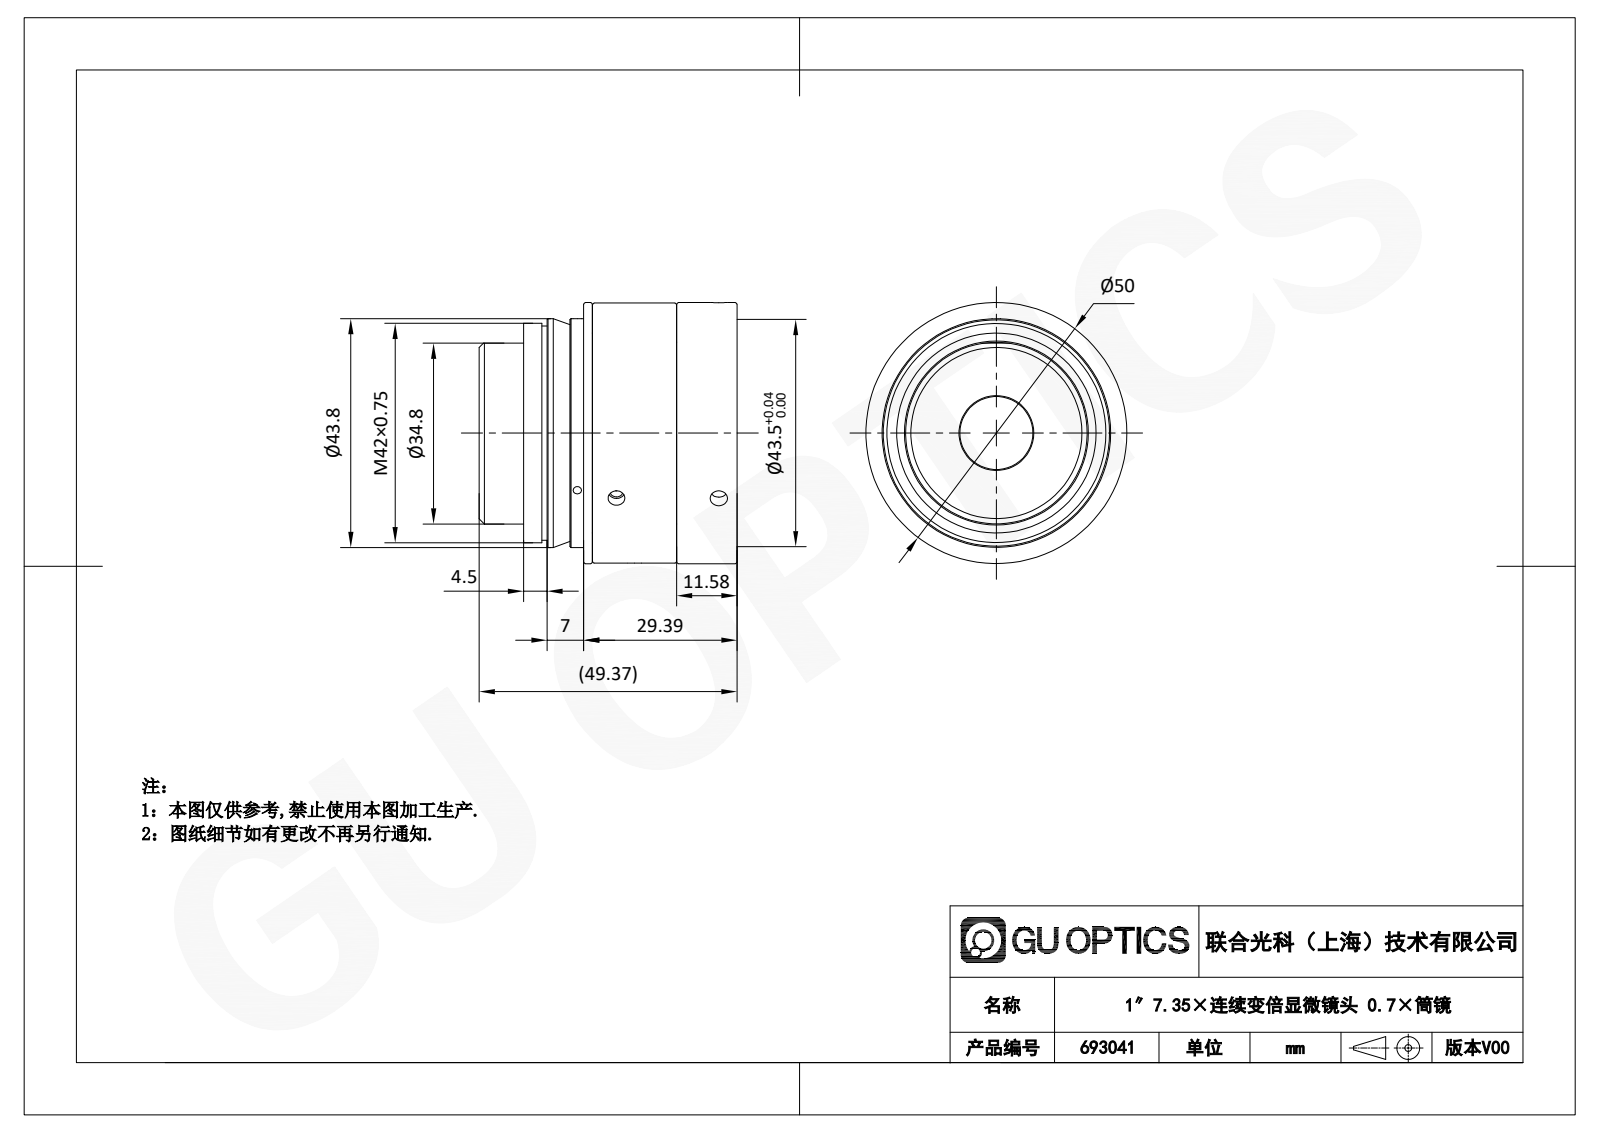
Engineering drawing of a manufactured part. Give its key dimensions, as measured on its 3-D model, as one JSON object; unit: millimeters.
{"part_name": "693041", "step_written_by": "SolidWorks 2020 (CONFIG_CONTROL_DESIGN)", "units": "millimeters", "bodies": {"solids": 0, "faces": 72, "planar": 22, "cylindrical": 28, "other": 22}, "overall_size": [50, 50, 49.37], "round_holes": [[2.5, 2], [3.2, 2], [2.7, 1], [14, 1], [25.5, 1], [40, 1], [41, 1], [42, 1], [43.8, 1], [50, 1]], "round_bosses_or_shafts": [[3.3, 3], [1.6, 3], [49.8, 1], [44.6, 1], [43.5, 1], [38.25, 1], [34.8, 1], [17.5, 1]], "partial_cylinders_radius": [[1.75, 1]], "face_to_face_distances": [38.97, 18.99, 19.98, 4.37, 14.62, 34.6, 10.4, 14.77, 29.39, 49.37]}
